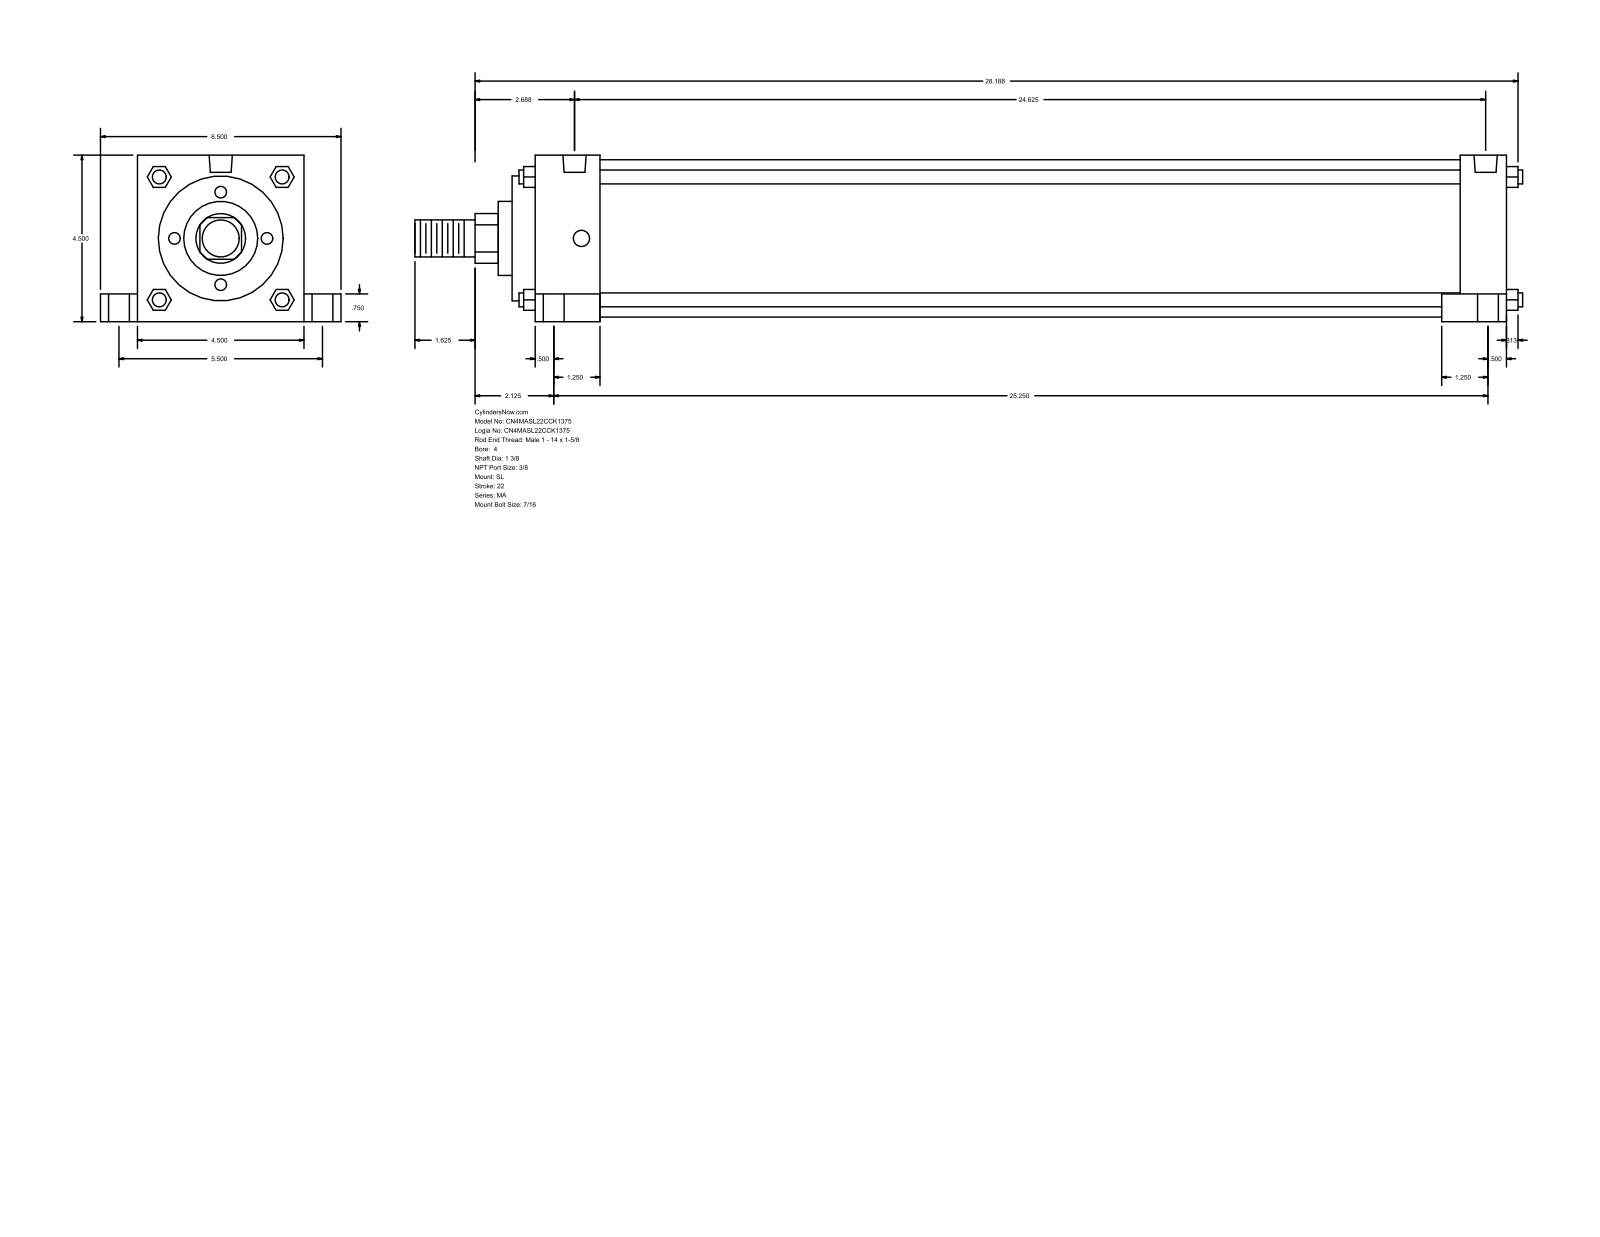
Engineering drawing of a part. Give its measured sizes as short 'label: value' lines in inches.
name: MA_SL__0400_1.375
written by: GSSL Pune (CONFIG_CONTROL_DESIGN)
unit: in
bodies: 0 solids, 150 faces (113 planar, 37 cylindrical, 0 other)
size: 29.937 × 6.5 × 4.5
holes: 4× ⌀0.437, 4× ⌀0.563, 4× ⌀0.813, 2× ⌀0.627
bosses: 4× ⌀0.375, 1× ⌀4.25, 1× ⌀3.375, 1× ⌀2, 1× ⌀1.375, 1× ⌀1
rounds: 1× R0.672
face distances: 4.5, 26.25, 23.25, 26.875, 0.625, 2.375, 1.75, 24.5, 25.625, 25
hole spacings: 2.751, 2.761, 2.807, 2.85, 5.5, 24.25, 24.654, 24.841
